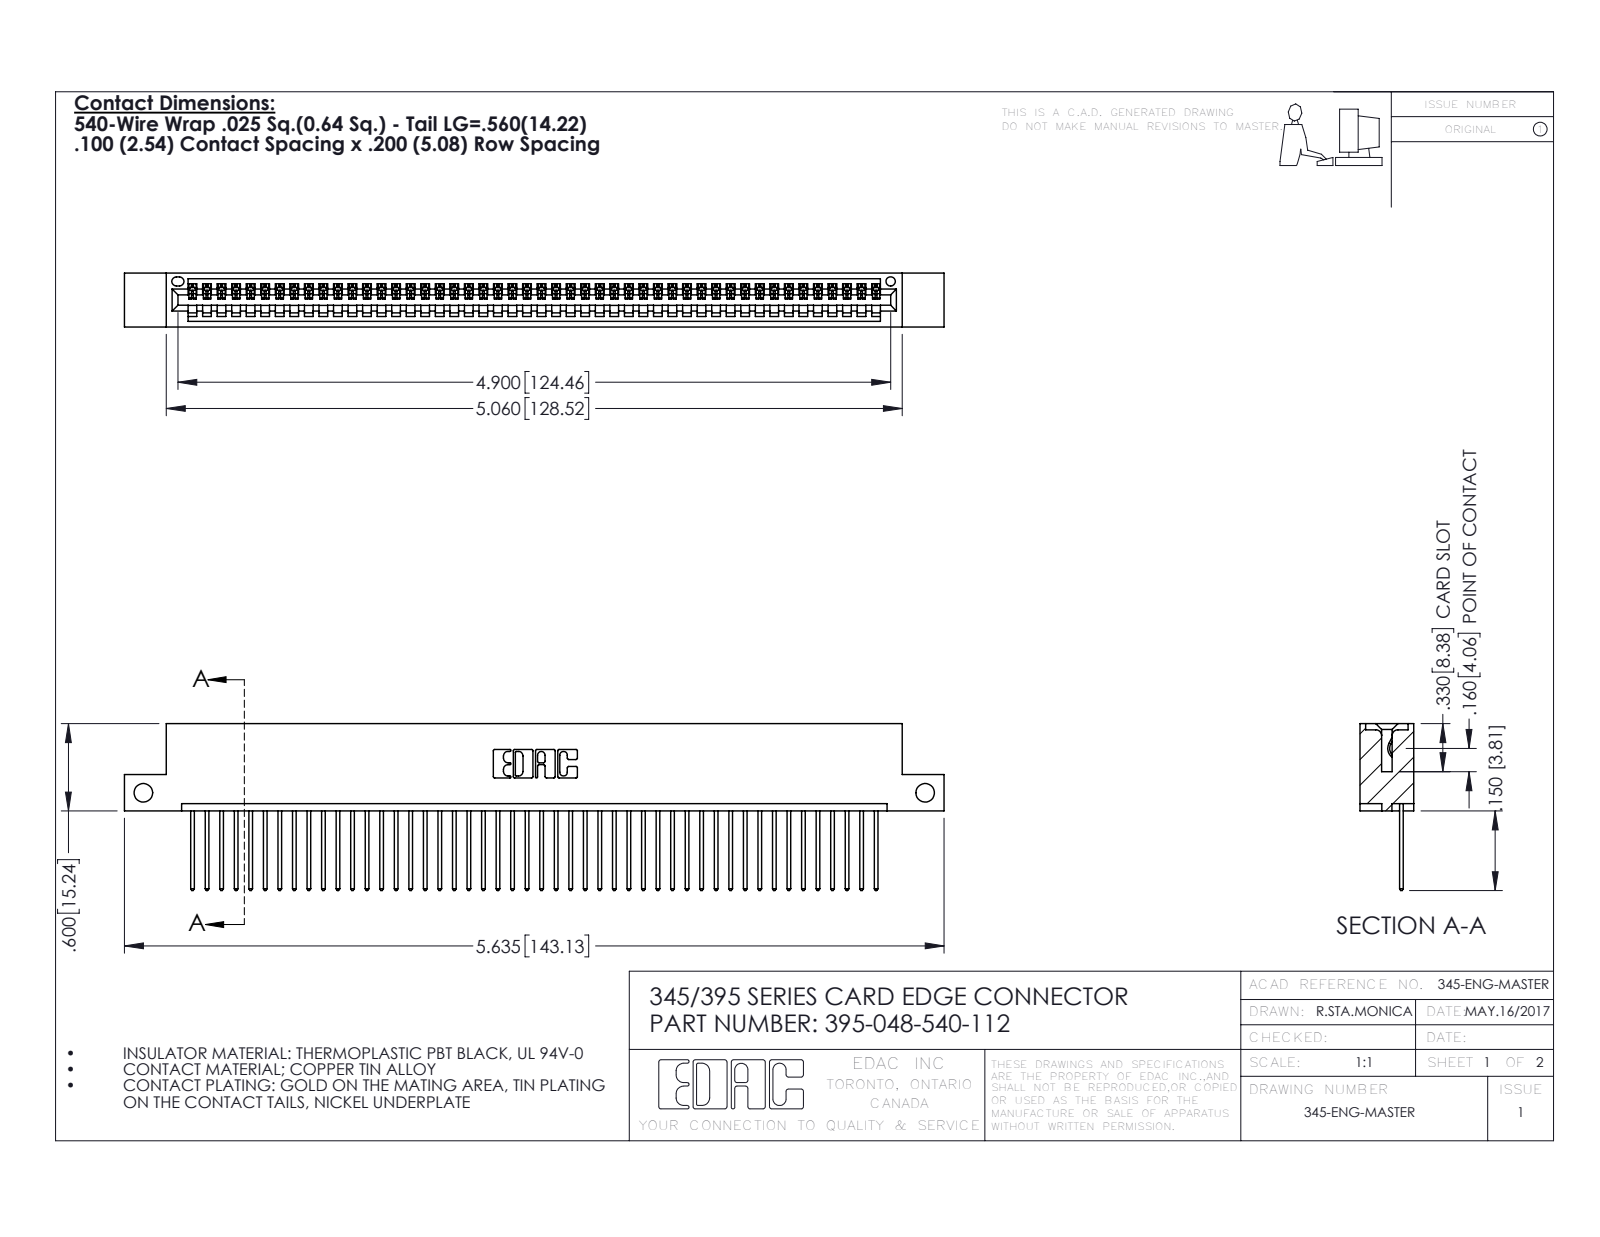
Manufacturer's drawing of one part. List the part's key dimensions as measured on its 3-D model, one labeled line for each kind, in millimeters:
Part name (STEP PRODUCT): 345-292-001_345-293-140; 345 Part_Flush Mounting Lugs - Side Mount; 395-048-540-112
STEP written by: SolidWorks 2016 (CONFIG_CONTROL_DESIGN)
Units: millimetres
Bodies: 49 solids, 2910 faces (2000 planar, 910 cylindrical, 0 other)
Overall size (bounding box): 143.1 × 29.1 × 9.4
Volume: 13 600 mm³ · Surface area: 18 510 mm²
Round holes (diameter × count): ⌀3.3 ×2, ⌀1.6 ×1
Partial cylindrical surfaces — rounded edges, fillets, slot ends (radius × count): R0.2 ×96, R0.3 ×96, R0.3 ×22, R0.2 ×6, R0.8 ×6, R0.7 ×3, R0.8 ×2, R1 ×2
Main face-to-face distances: 7.6, 1.8, 9.4, 2.5, 6.9, 0.6, 5.1, 5.7, 3.8, 1.8
Hole centre spacings: 136.5
